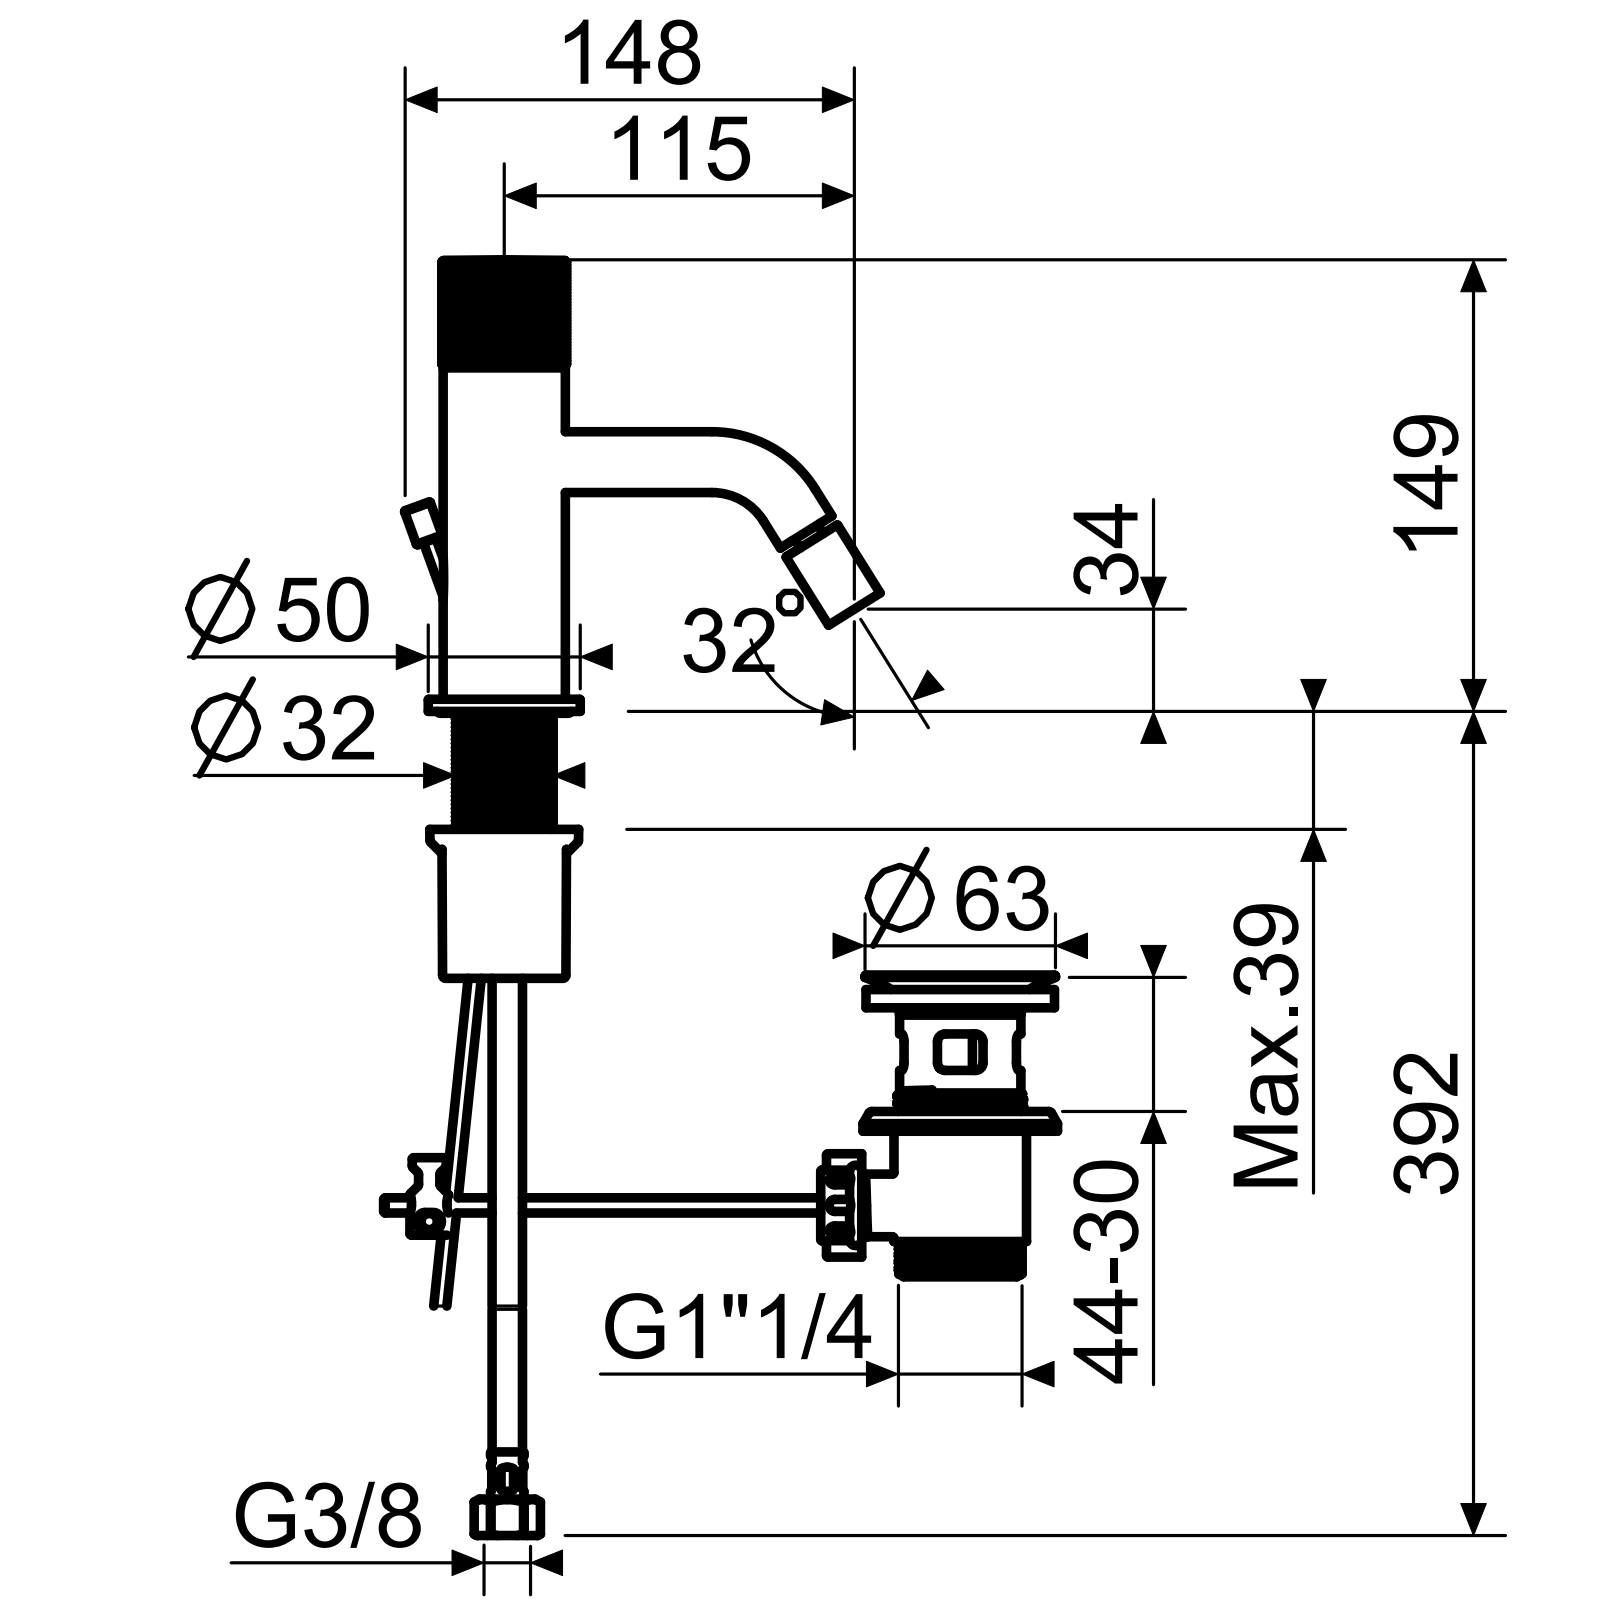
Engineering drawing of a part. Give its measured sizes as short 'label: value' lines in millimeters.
name: ALOG005C006; los0053.stp; ALOG300C001; ALOG007C004 (+8 more)
written by: Shapr3D (AUTOMOTIVE_DESIGN)
unit: mm
bodies: 14 solids, 6573 faces (3032 planar, 1233 cylindrical, 2308 other)
size: 156.42 × 149.61 × 50
volume: 79 821 mm³; area: 73 635 mm²
holes: 2× ⌀4.2, 1× ⌀5, 1× ⌀5.1, 1× ⌀5.3, 1× ⌀6.5, 1× ⌀8, 1× ⌀9, 1× ⌀10.3, 1× ⌀11.8, 1× ⌀12.2, 1× ⌀13, 1× ⌀13.5
bosses: 2× ⌀20, 2× ⌀9, 1× ⌀50, 1× ⌀40.2, 1× ⌀37.8, 1× ⌀32, 1× ⌀18, 1× ⌀16.5
rounds: 2× R1, 2× R2.5, 2× R3, 1× R1.5, 1× R4, 1× R6.5, 1× R10, 1× R16
face distances: 2, 4, 146.33, 142.33, 2.75, 144.33, 100.33, 110.95, 108.95, 106.95
hole spacings: 0.59
